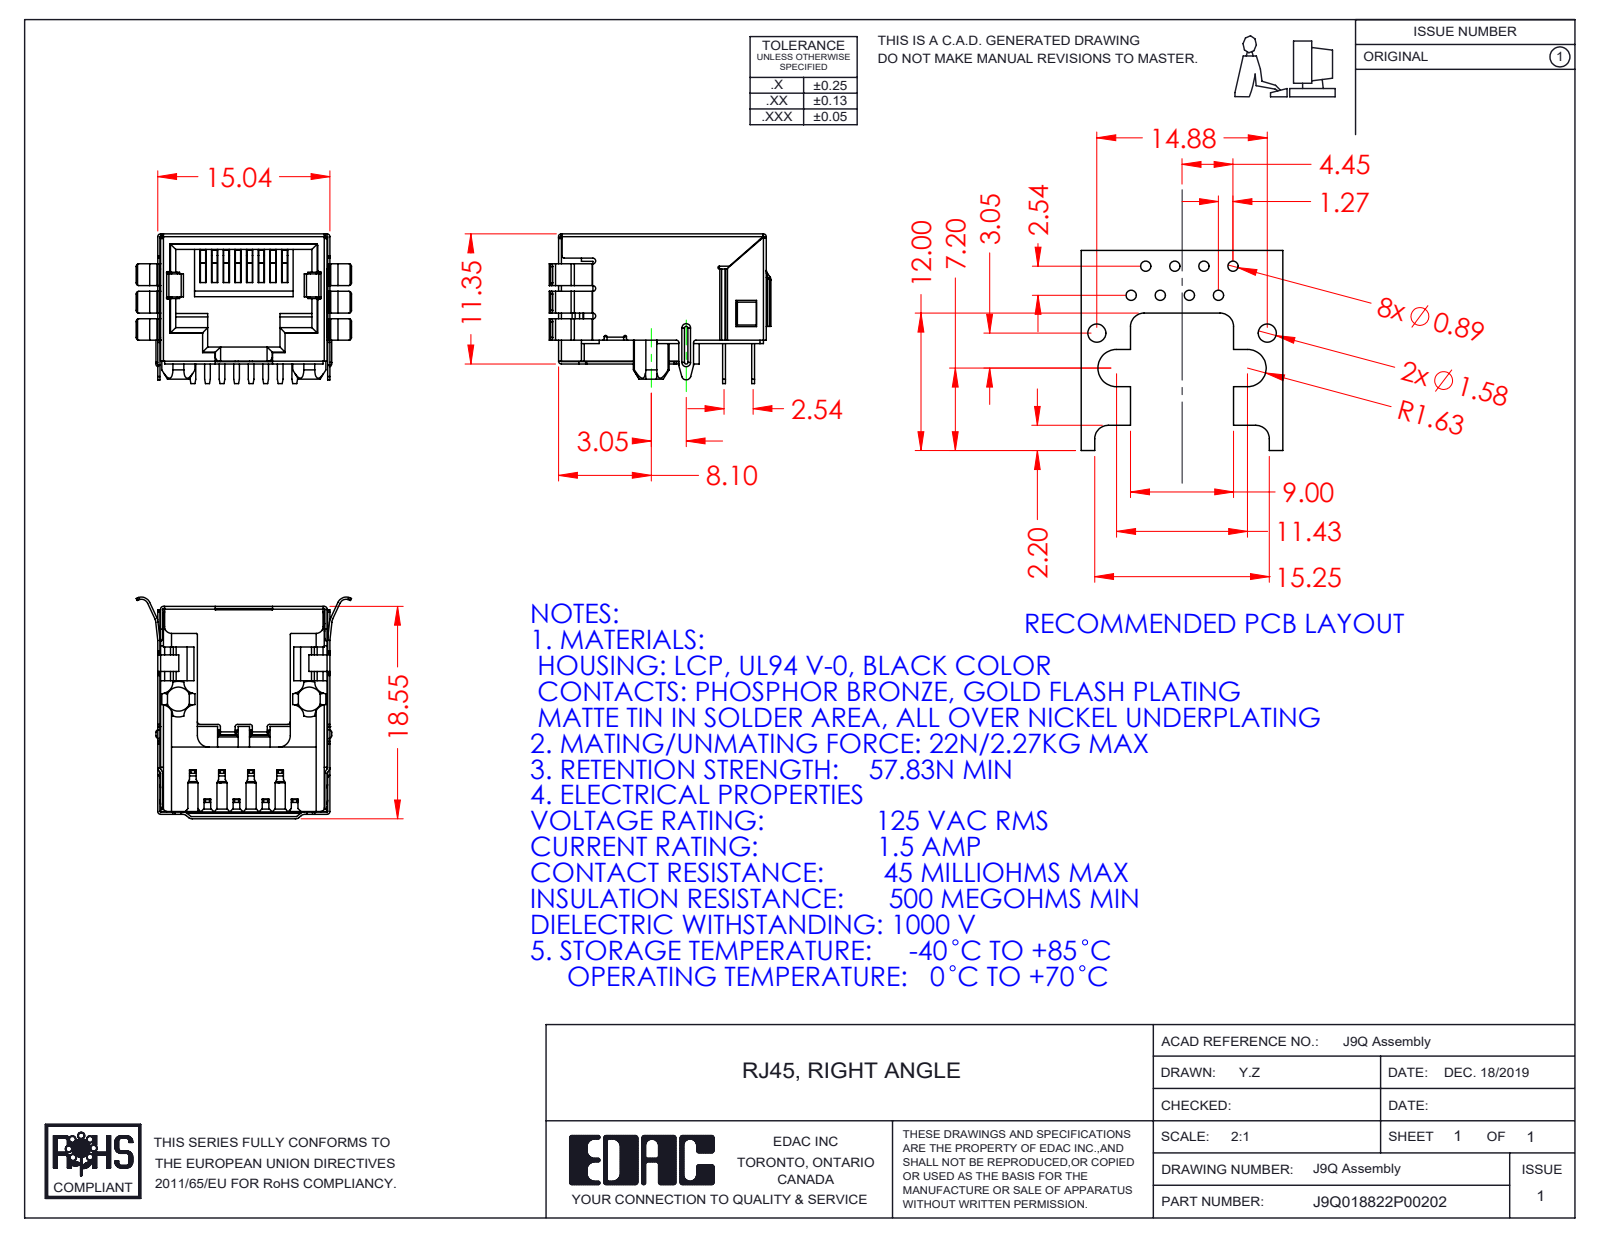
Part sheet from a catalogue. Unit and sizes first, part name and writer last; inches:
Units: inches
Overall size (bounding box): 0.762 × 0.741 × 0.515
Partial cylindrical surfaces — rounded edges, fillets, slot ends (radius × count): R0.004 ×43, R0.008 ×35, R0.01 ×34, R0.006 ×24, R0.02 ×19, R0.012 ×14, R0.024 ×8, R0.041 ×8
Main face-to-face distances: 0.574, 0.572, 0.584, 0.565, 0.582, 0.02, 0.439, 0.563, 0.576, 0.592
Volume: 0.073 in³ · Surface area: 7.468 in²
Bodies: 11 solids, 1339 faces (949 planar, 369 cylindrical, 21 other)
Part name (STEP PRODUCT): 9Q Insulator; J9Q018822P00202; 9Q Contact Lock; 9Q Contacts (+1 more)
STEP written by: SolidWorks 2016 (CONFIG_CONTROL_DESIGN)
